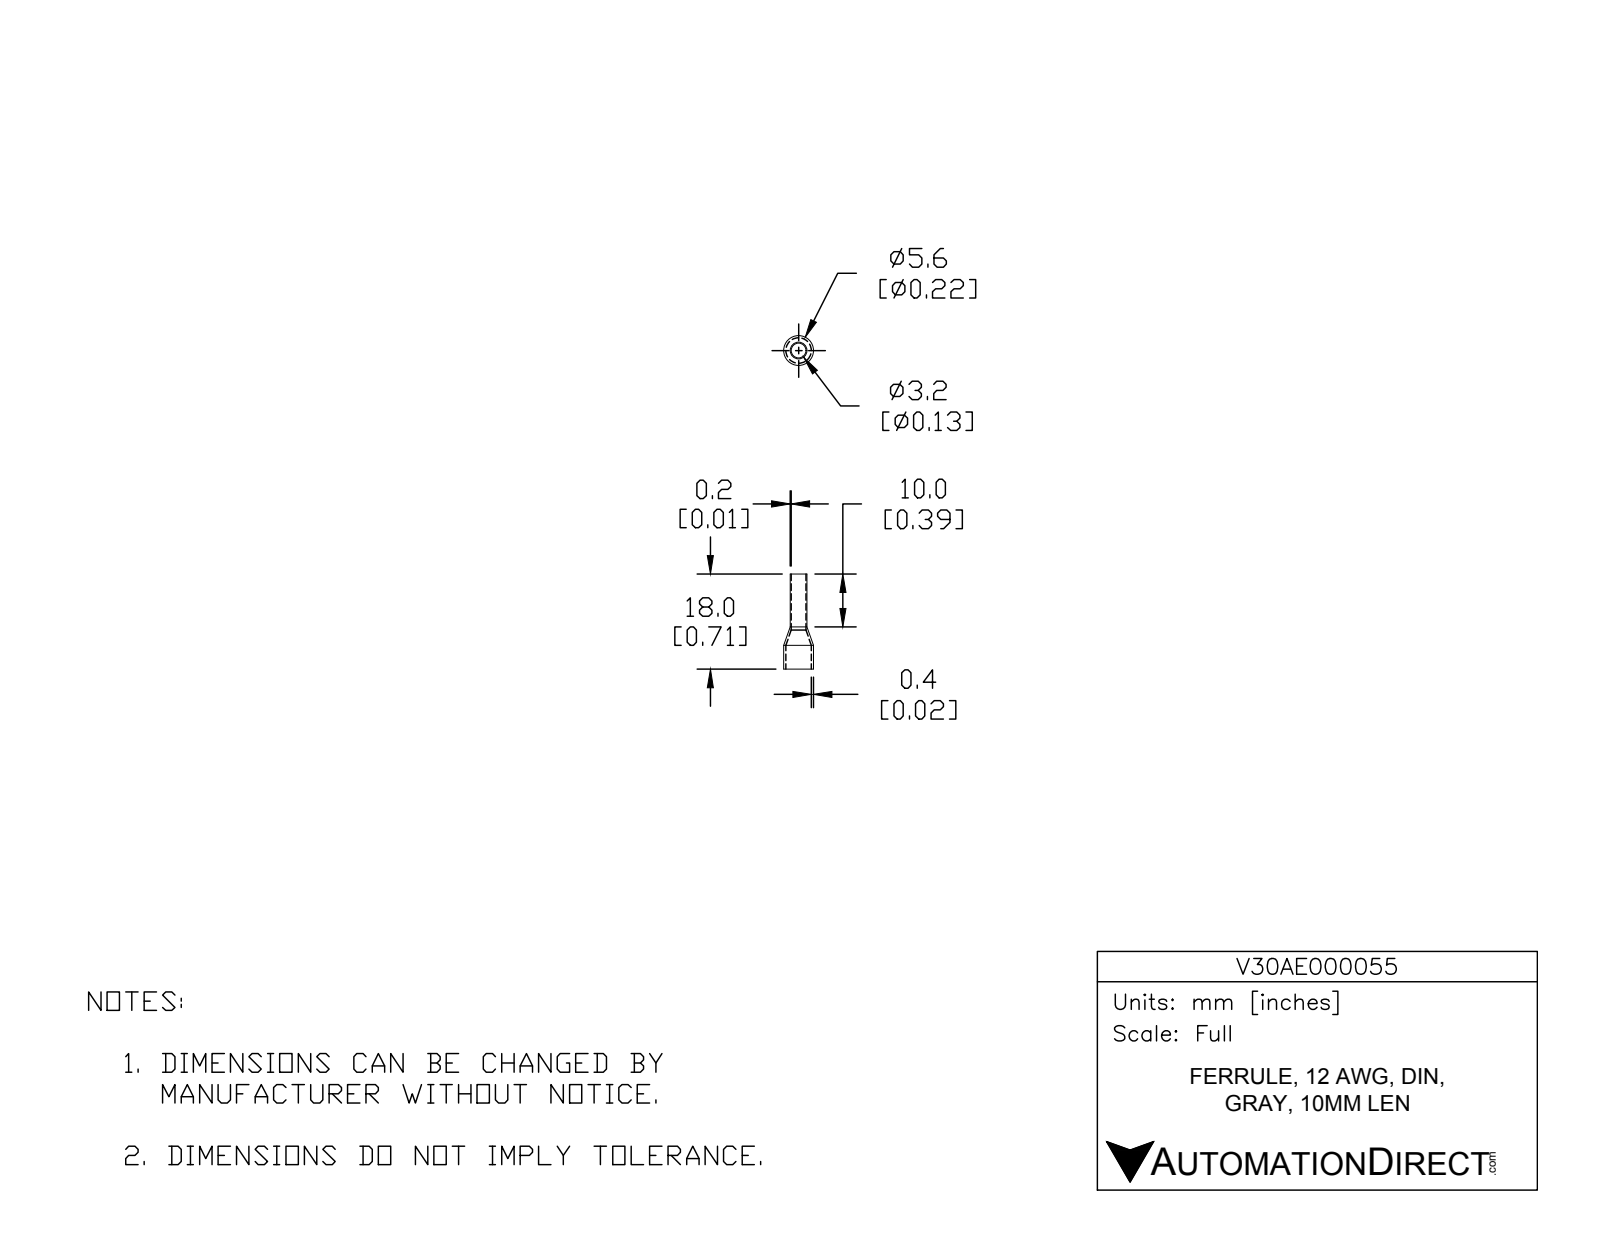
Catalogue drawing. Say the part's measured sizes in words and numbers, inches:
The part is named "V30AE000055". Its 3-D file was written by "SolidWorks 2017 (AUTOMOTIVE_DESIGN)". It is 1 solid with 14 faces: 2 planar, 8 cylindrical and 4 other. Overall it measures 0.709 by 0.22 by 0.22 inches. Its volume is 0.004 cubic inches and its surface area 0.677 square inches. Round holes: 1 of diameter 0.11, 1 of diameter 0.189. Round bosses or shafts: 1 of diameter 0.22, 1 of diameter 0.126. The main face-to-face distances are 0.709.
